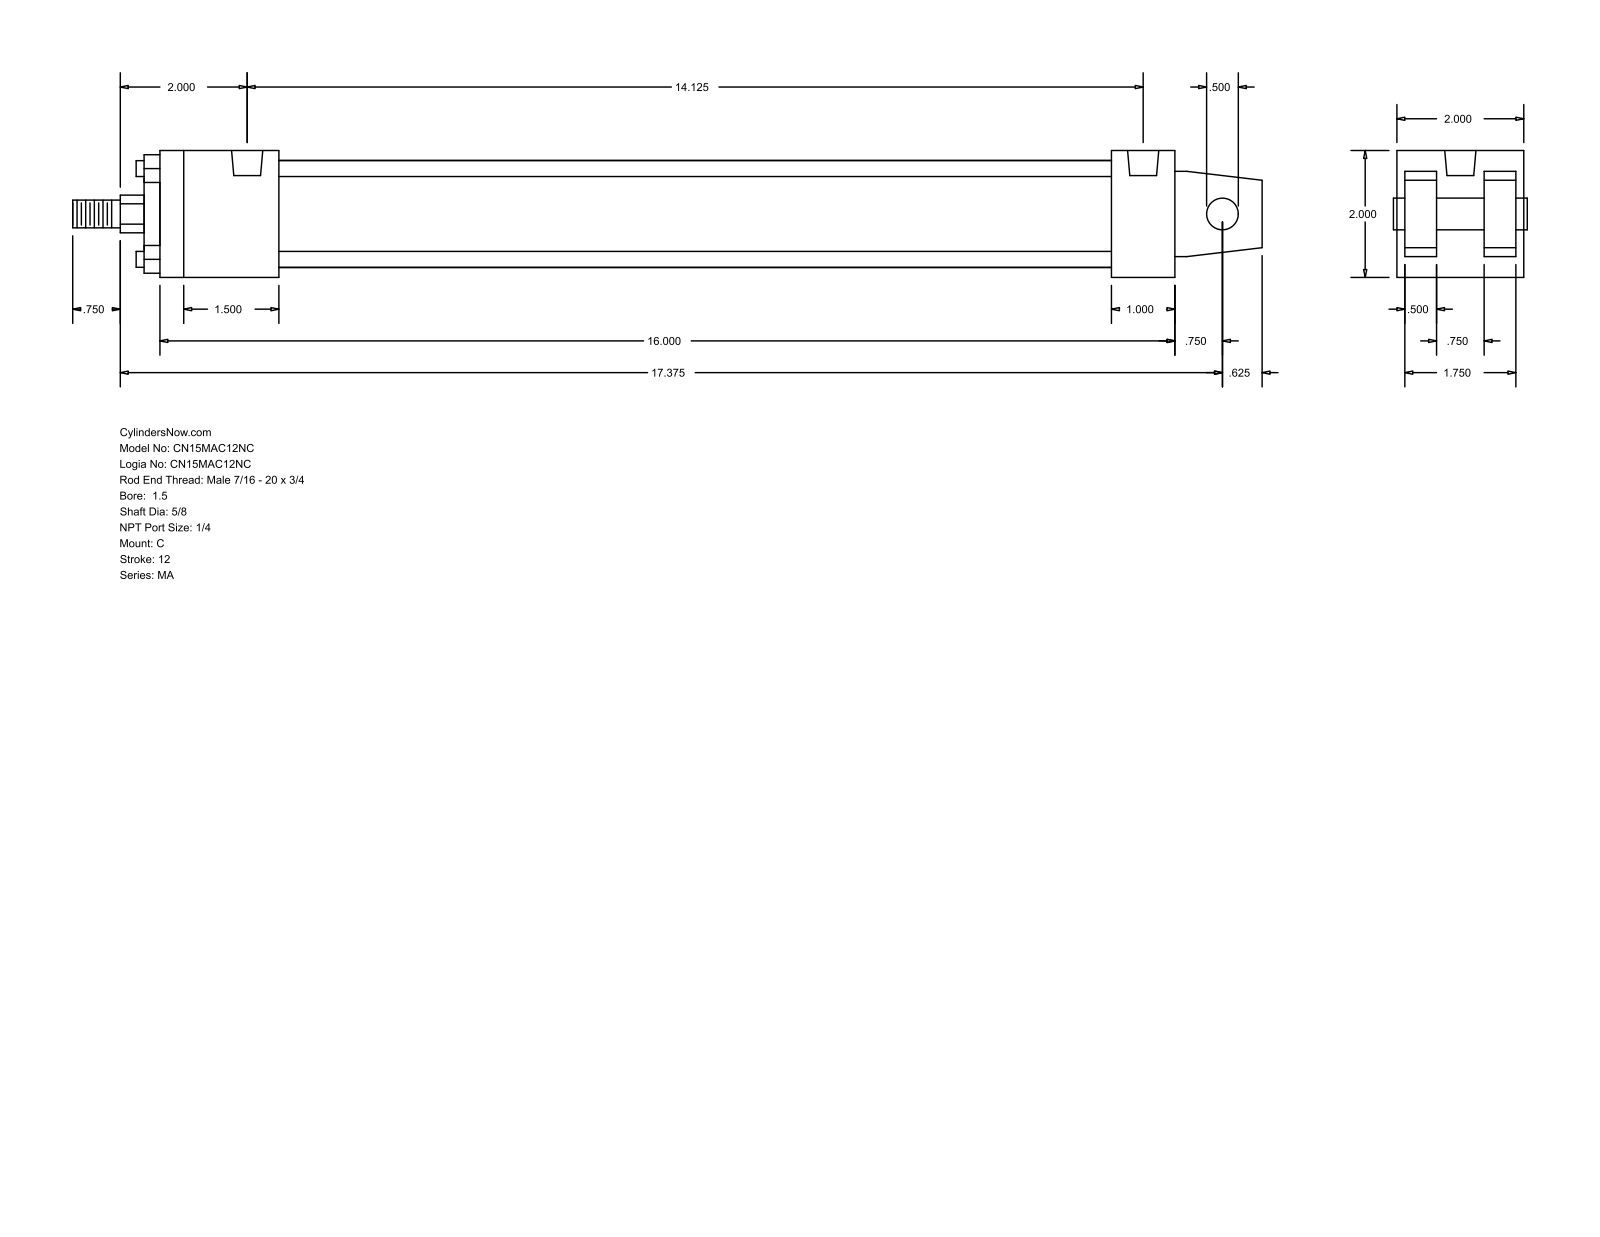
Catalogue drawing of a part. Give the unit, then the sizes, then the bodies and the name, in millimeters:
Units: millimetres
Overall size (bounding box): 476.25 × 50.8 × 50.8
Round holes (diameter × count): ⌀7.94 ×4, ⌀12.49 ×2
Round bosses / shafts (diameter × count): ⌀6.35 ×4, ⌀42.93 ×1, ⌀28.57 ×1, ⌀15.88 ×1, ⌀12.7 ×1, ⌀11.11 ×1
Partial cylindrical surfaces — rounded edges, fillets, slot ends (radius × count): R7.54 ×1
Main face-to-face distances: 50.8, 34.93, 12.7, 15.87, 3.17, 47.63, 31.76, 406.39, 381, 25.39
Hole centre spacings: 358.77
Bodies: 0 solids, 103 faces (76 planar, 27 cylindrical, 0 other)
Part name (STEP PRODUCT): MA_C__0150_0.625
STEP written by: GSSL Pune (CONFIG_CONTROL_DESIGN)
